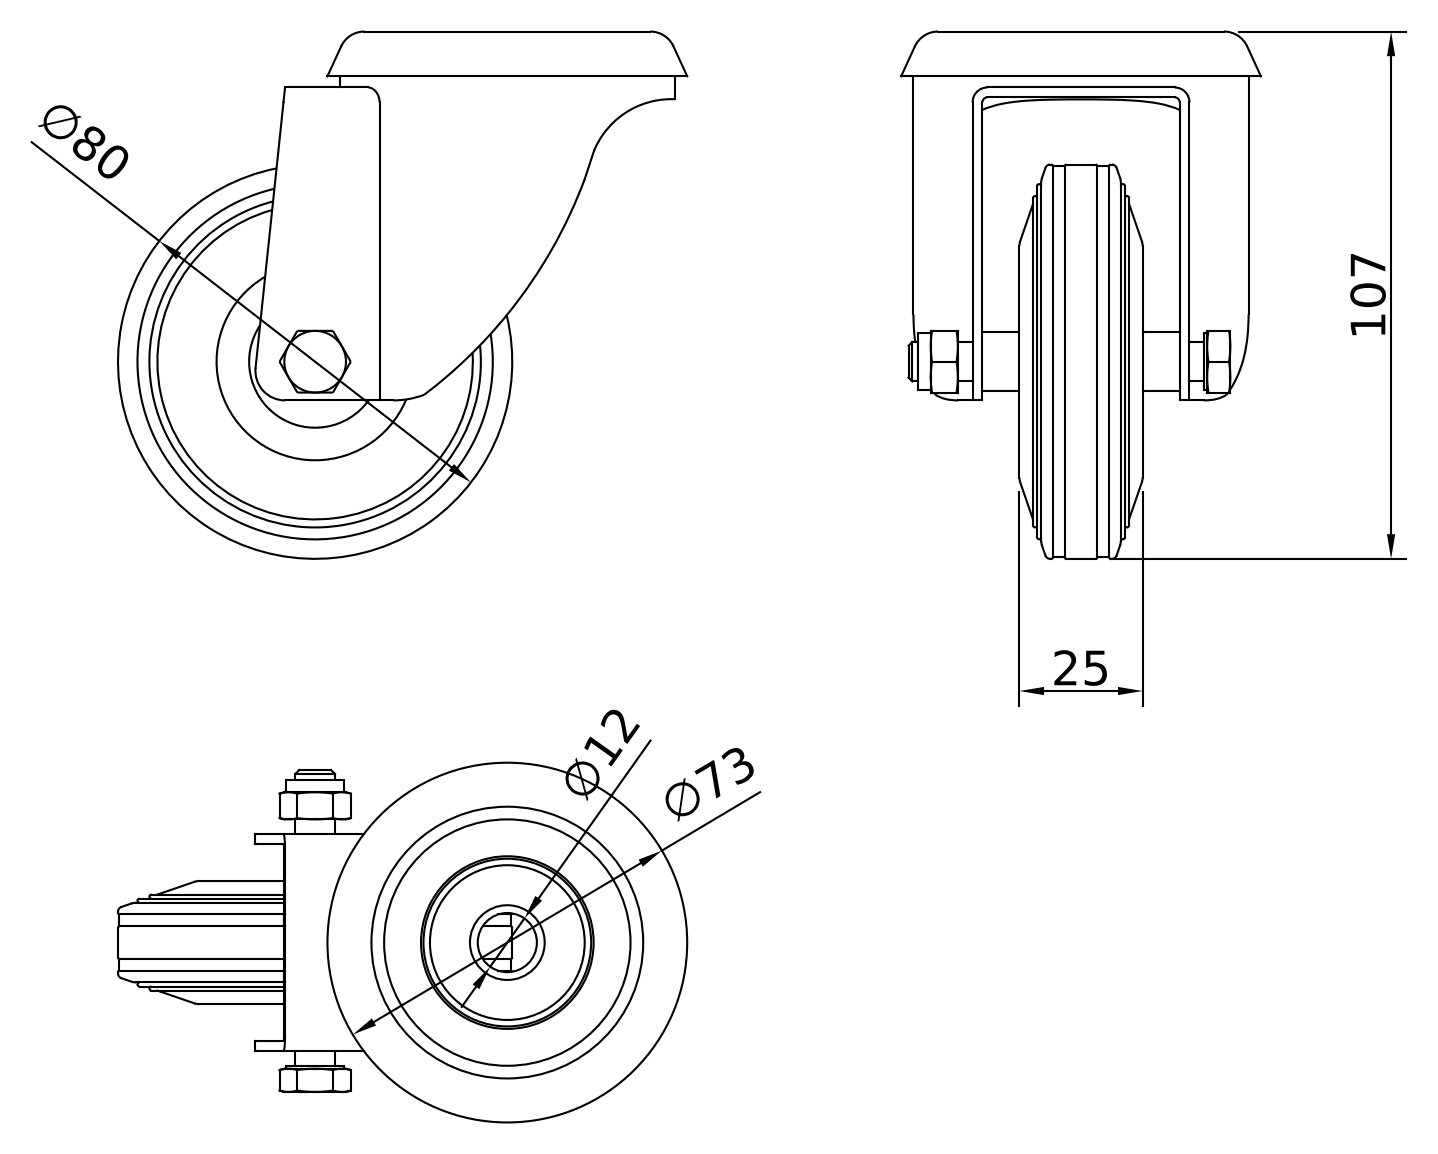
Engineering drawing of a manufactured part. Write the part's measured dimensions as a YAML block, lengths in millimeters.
part_name: "CRUST0000192; 440000025812; 440000025813; 440000025811"
step_written_by: "Autodesk Inventor 2022 (AUTOMOTIVE_DESIGN)"
units: millimeters
bodies: {solids: 3, faces: 138, planar: 50, cylindrical: 29, other: 59}
overall_size: [115.5, 107, 73]
volume: 147006
surface_area: 48737
round_holes:
  - {diameter: 12, count: 2}
  - {diameter: 9, count: 1}
  - {diameter: 64, count: 1}
round_bosses_or_shafts:
  - {diameter: 80, count: 1}
  - {diameter: 79.4, count: 1}
  - {diameter: 68, count: 1}
  - {diameter: 34.03, count: 1}
  - {diameter: 11.63, count: 1}
  - {diameter: 8, count: 1}
partial_cylinders:
  - {radius: 1, count: 2}
  - {radius: 3, count: 2}
  - {radius: 6, count: 1}
  - {radius: 17, count: 1}
  - {radius: 18, count: 1}
  - {radius: 97.5, count: 1}
face_to_face_distances: [2, 42, 7.5, 9.5, 34.5, 32.5, 40, 44, 7.35, 13.09]
